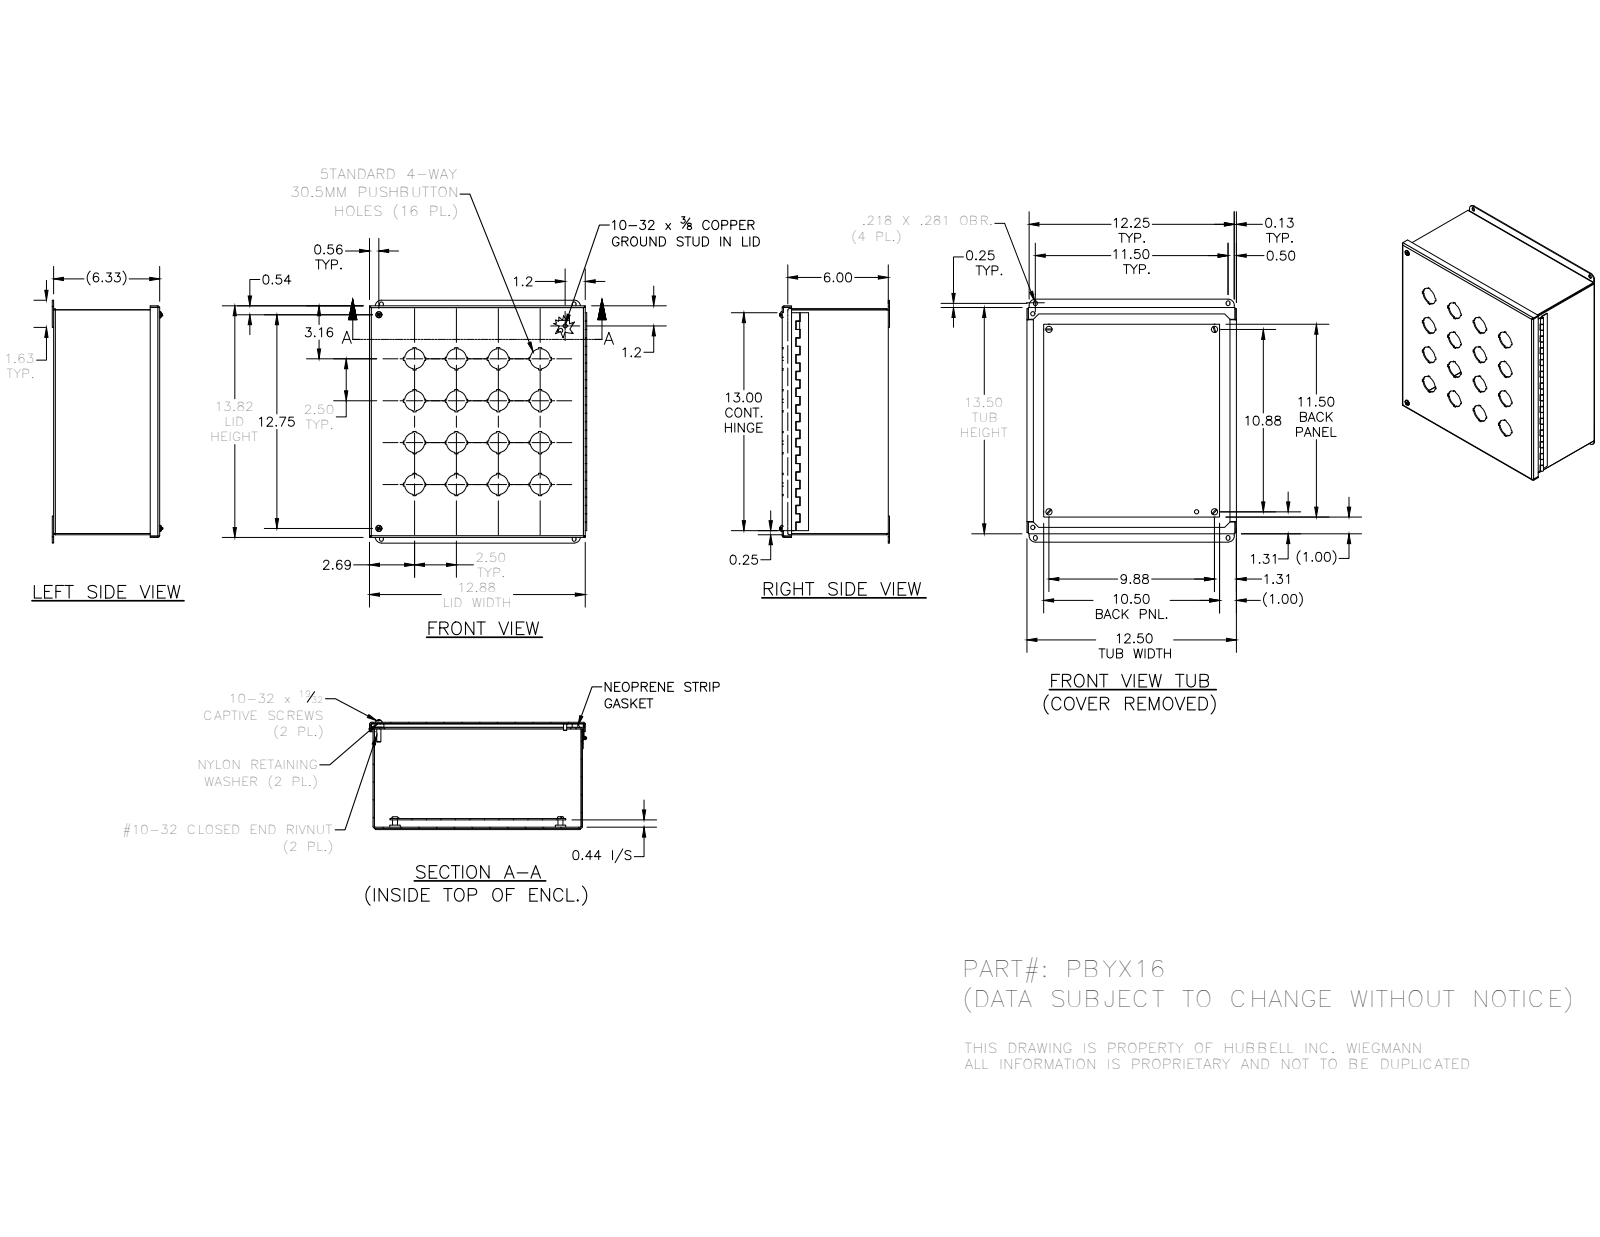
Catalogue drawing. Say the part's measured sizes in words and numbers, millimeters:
The part is named "PBYX16LID; 39077; 316274; PBYX16BKP (+8 more)". Its 3-D file was written by "Autodesk Inventor 2016 (AUTOMOTIVE_DESIGN)". It is 25 solids with 854 faces: 547 planar, 216 cylindrical and 91 other. Overall it measures 368.3 by 329.29 by 166.01 millimeters. Its volume is 1 143 000 cubic millimeters and its surface area 1 189 000 square millimeters. Round holes: 16 of diameter 30.48, 6 of diameter 3.96, 4 of diameter 7.94, 2 of diameter 4.98, 2 of diameter 6.53, 2 of diameter 7.06, 2 of diameter 7.14, 1 of diameter 2.96, 1 of diameter 6.35. Round bosses or shafts: 7 of diameter 4.83, 6 of diameter 9.47, 4 of diameter 15.88, 4 of diameter 7.62, 2 of diameter 11.51, 2 of diameter 10.31, 2 of diameter 6.3, 1 of diameter 6.35. Partial cylindrical surfaces (rounded edges, fillets, slot ends): 12 of radius 0.79, 12 of radius 2.67, 8 of radius 2.77, 8 of radius 3.17, 4 of radius 9.53, 2 of radius 2.27. The main face-to-face distances are 1.88, 158.95, 145.97, 12.98, 160.83, 14.86, 315.62, 157.07, 341.02, 144.09. The hole center spacings are 63.5, 141.99, 89.8, 127, 200.8, 179.61, 190.5, 228.95.
